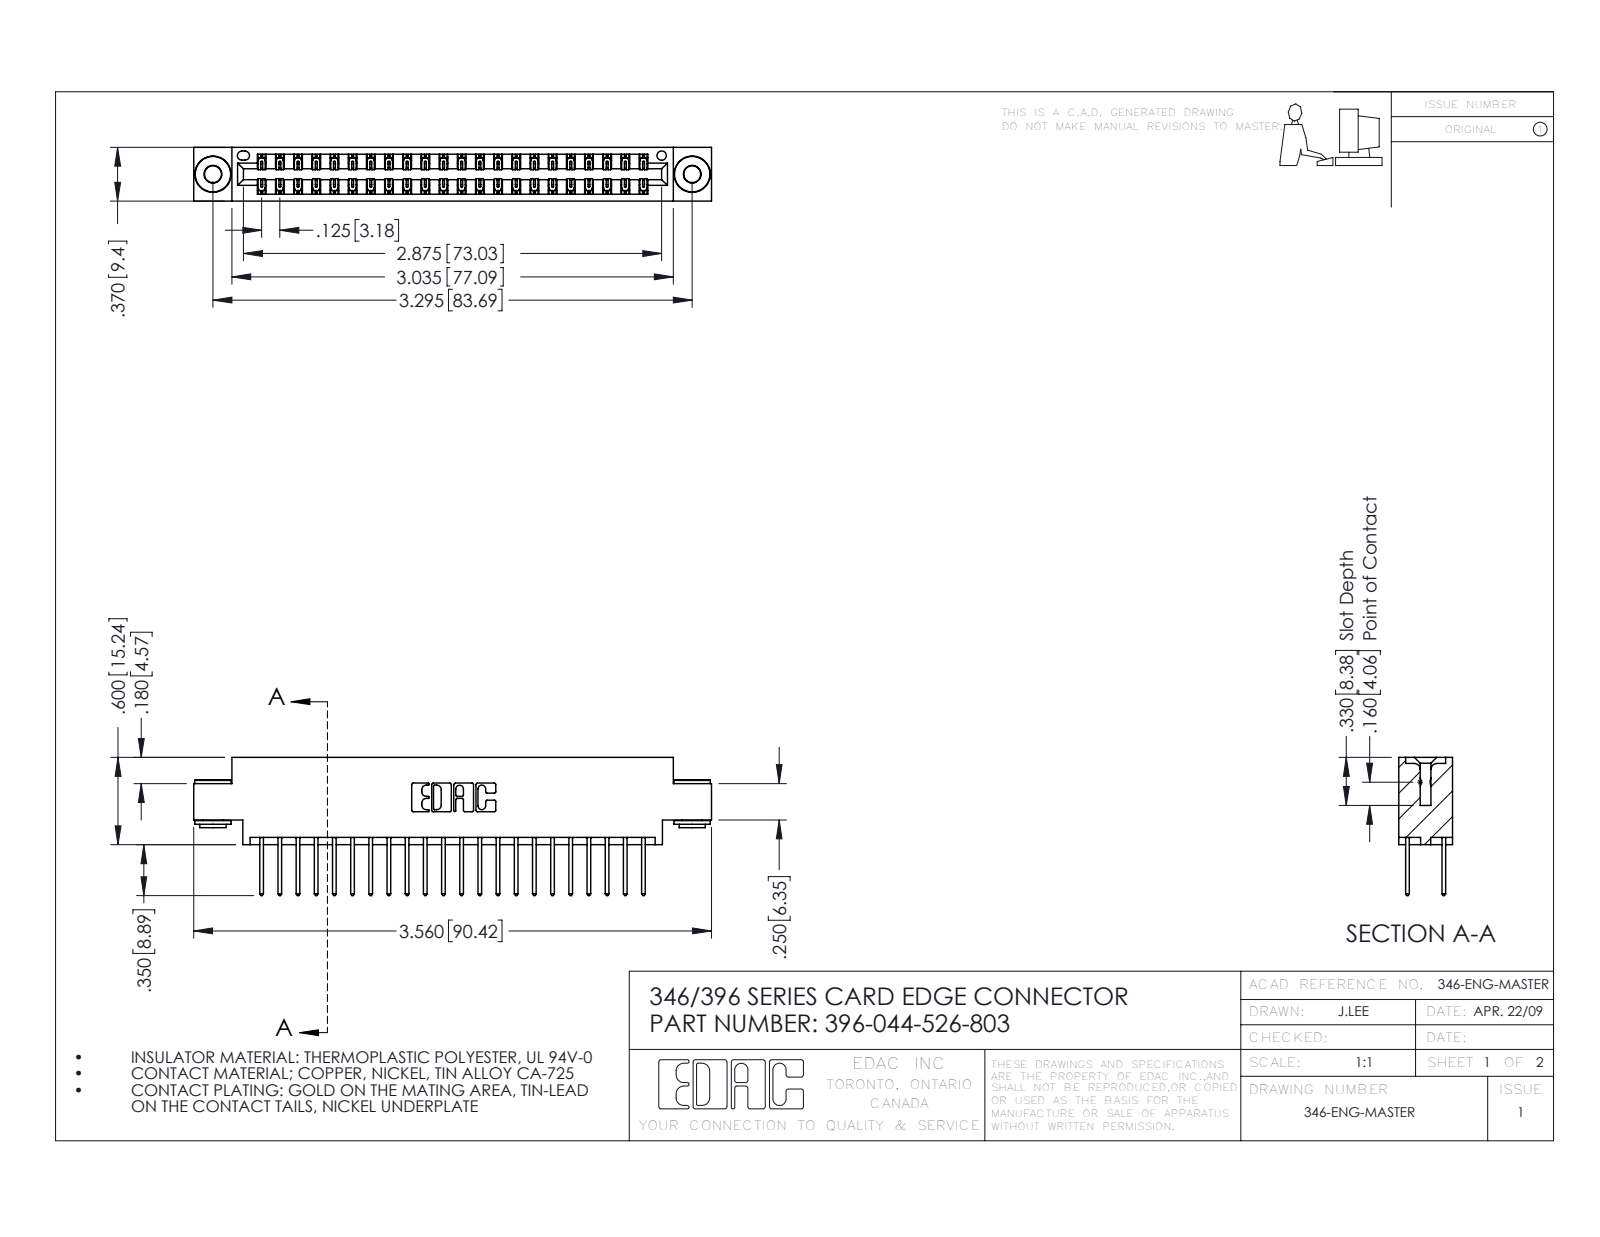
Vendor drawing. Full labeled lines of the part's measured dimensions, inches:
Part name (STEP PRODUCT): 345-250-002_345-250-002-102; 345-292-001_345-293-126; 346 Part_0.170 Offset - 0.156 Dia-TH; 396-044-526-803
STEP written by: SolidWorks 2016 (CONFIG_CONTROL_DESIGN)
Units: inches
Bodies: 47 solids, 2452 faces (1630 planar, 814 cylindrical, 8 other)
Overall size (bounding box): 3.56 × 0.95 × 0.37
Volume: 0.525 in³ · Surface area: 18.94 in²
Round holes (diameter × count): ⌀0.116 ×2, ⌀0.156 ×2, ⌀0.064 ×1
Round bosses / shafts (diameter × count): ⌀0.25 ×2, ⌀0.18 ×2, ⌀0.136 ×2
Partial cylindrical surfaces — rounded edges, fillets, slot ends (radius × count): R0.006 ×66, R0.01 ×44, R0.01 ×22, R0.007 ×6, R0.031 ×6, R0.026 ×3, R0.014 ×2, R0.022 ×2
Main face-to-face distances: 0.048, 0.322, 0.25, 0.37, 0.025, 0.072, 0.298, 0.275, 0.148, 0.222
Hole centre spacings: 0.246, 3.087, 3.295
